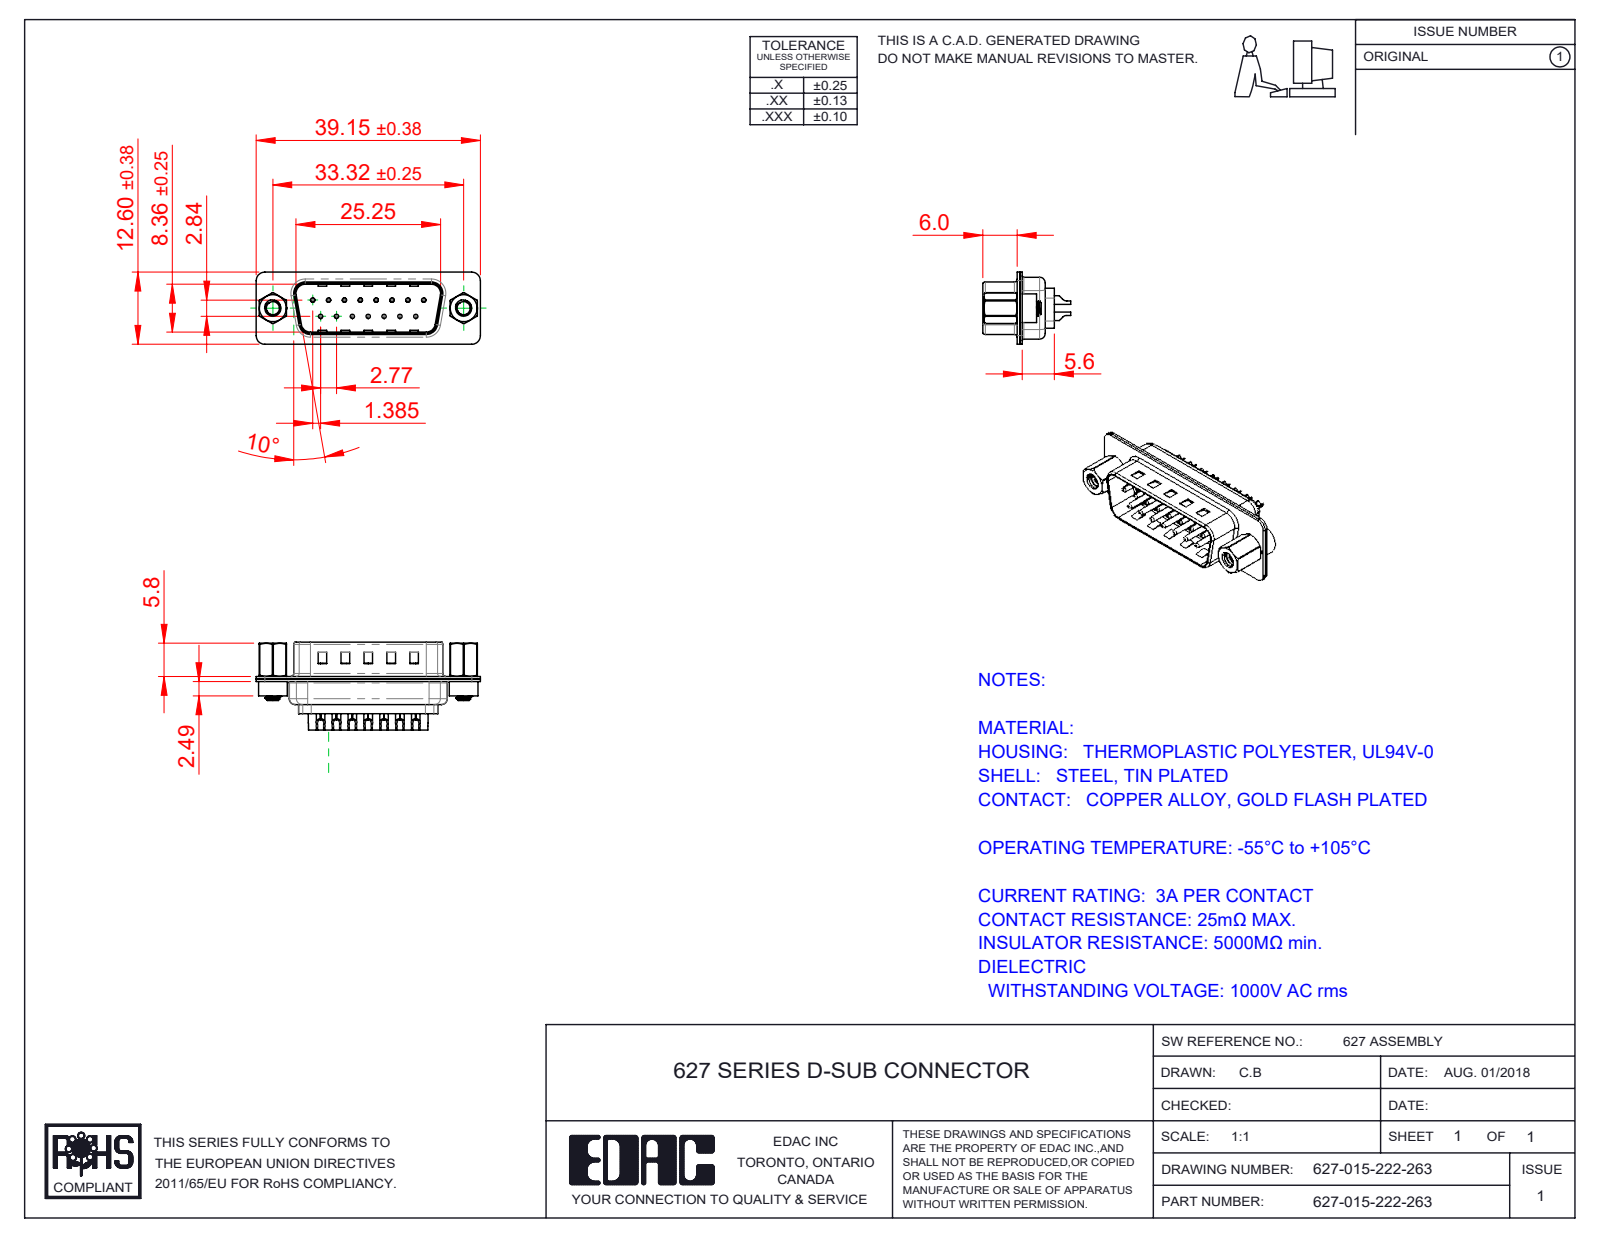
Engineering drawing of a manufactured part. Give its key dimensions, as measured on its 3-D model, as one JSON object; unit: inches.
{"part_name": "627-015-222-263; 627 Contact Row 1_22L; 627 Housing_15 LP; 627 Shell Front_15 Contacts (+4 more)", "step_written_by": "SolidWorks 2020 (CONFIG_CONTROL_DESIGN)", "units": "inches", "bodies": {"solids": 22, "faces": 1422, "planar": 371, "cylindrical": 638, "other": 413}, "overall_size": [1.541, 0.604, 0.496], "volume_in3": 0.125, "surface_area_in2": 9.137, "round_holes": [[0.014, 15], [0.043, 15], [0.063, 15], [0.089, 2], [0.09, 2], [0.157, 2], [0.189, 2]], "round_bosses_or_shafts": [[0.079, 15], [0.059, 15], [0.03, 15], [0.197, 2], [0.193, 2], [0.11, 2]], "partial_cylinders_radius": [[0.059, 16], [0.079, 12], [0.02, 8], [0.063, 8], [0.039, 6], [0.01, 4], [0.024, 4], [0.026, 4]], "face_to_face_distances": [0.016, 0.018, 0.035, 0.032, 0.377, 0.345, 0.059, 0.055, 0.256, 0.22], "hole_center_spacings": [0.124, 0.109, 0.218, 0.327, 0.436, 0.198, 0.198, 0.294]}
